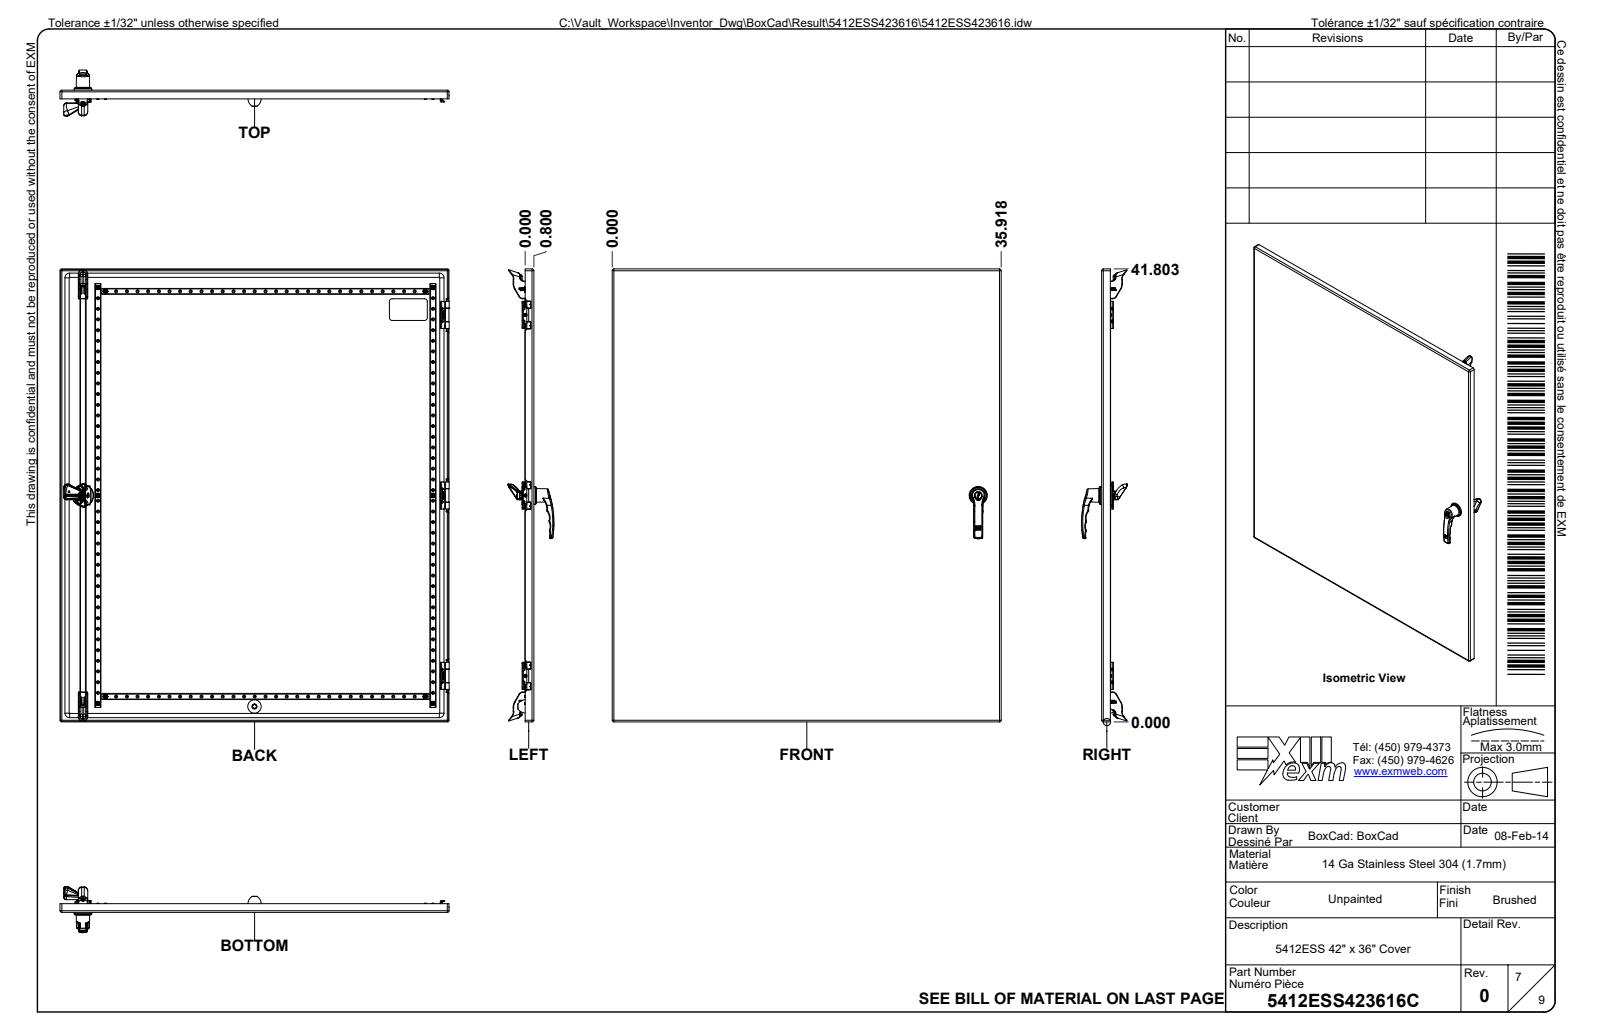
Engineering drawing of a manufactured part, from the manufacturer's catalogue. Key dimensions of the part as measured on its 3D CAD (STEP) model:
Part name (STEP PRODUCT): 5412ESS423616; 5412ESS423616B; 5412ESS423616B-P; STK-Q-16020 (+8 more)
STEP written by: Autodesk Inventor 2024 (AUTOMOTIVE_DESIGN)
Units: inches
Bodies: 115 solids, 19259 faces (5812 planar, 4144 cylindrical, 9303 other)
Overall size (bounding box): 42 × 36.007 × 18.985
Volume: 581.6 in³ · Surface area: 15 449 in²
Round holes (diameter × count): ⌀0.165 ×76, ⌀0.03 ×18, ⌀0.315 ×14, ⌀0.201 ×12, ⌀0.311 ×11, ⌀0.27 ×8, ⌀0.29 ×7, ⌀0.044 ×6, ⌀0.197 ×6, ⌀0.268 ×6, ⌀0.5 ×5, ⌀0.39 ×4
Round bosses / shafts (diameter × count): ⌀0.237 ×76, ⌀0.03 ×18, ⌀0.232 ×16, ⌀0.039 ×12, ⌀0.717 ×8, ⌀0.311 ×8, ⌀0.262 ×8, ⌀0.177 ×7
Partial cylindrical surfaces — rounded edges, fillets, slot ends (radius × count): R0.02 ×247, R0.039 ×241, R0.01 ×170, R0.008 ×104, R0.079 ×55, R0.016 ×37, R0.012 ×36, R0.059 ×36
Main face-to-face distances: 0.068, 17.052, 16.984, 17.12, 16.178, 0.942, 0.874, 16.11, 0.105, 1.047
Hole centre spacings: 1.969, 0.984, 2.953, 3.937, 16.652, 4.921, 1.591, 5.906
